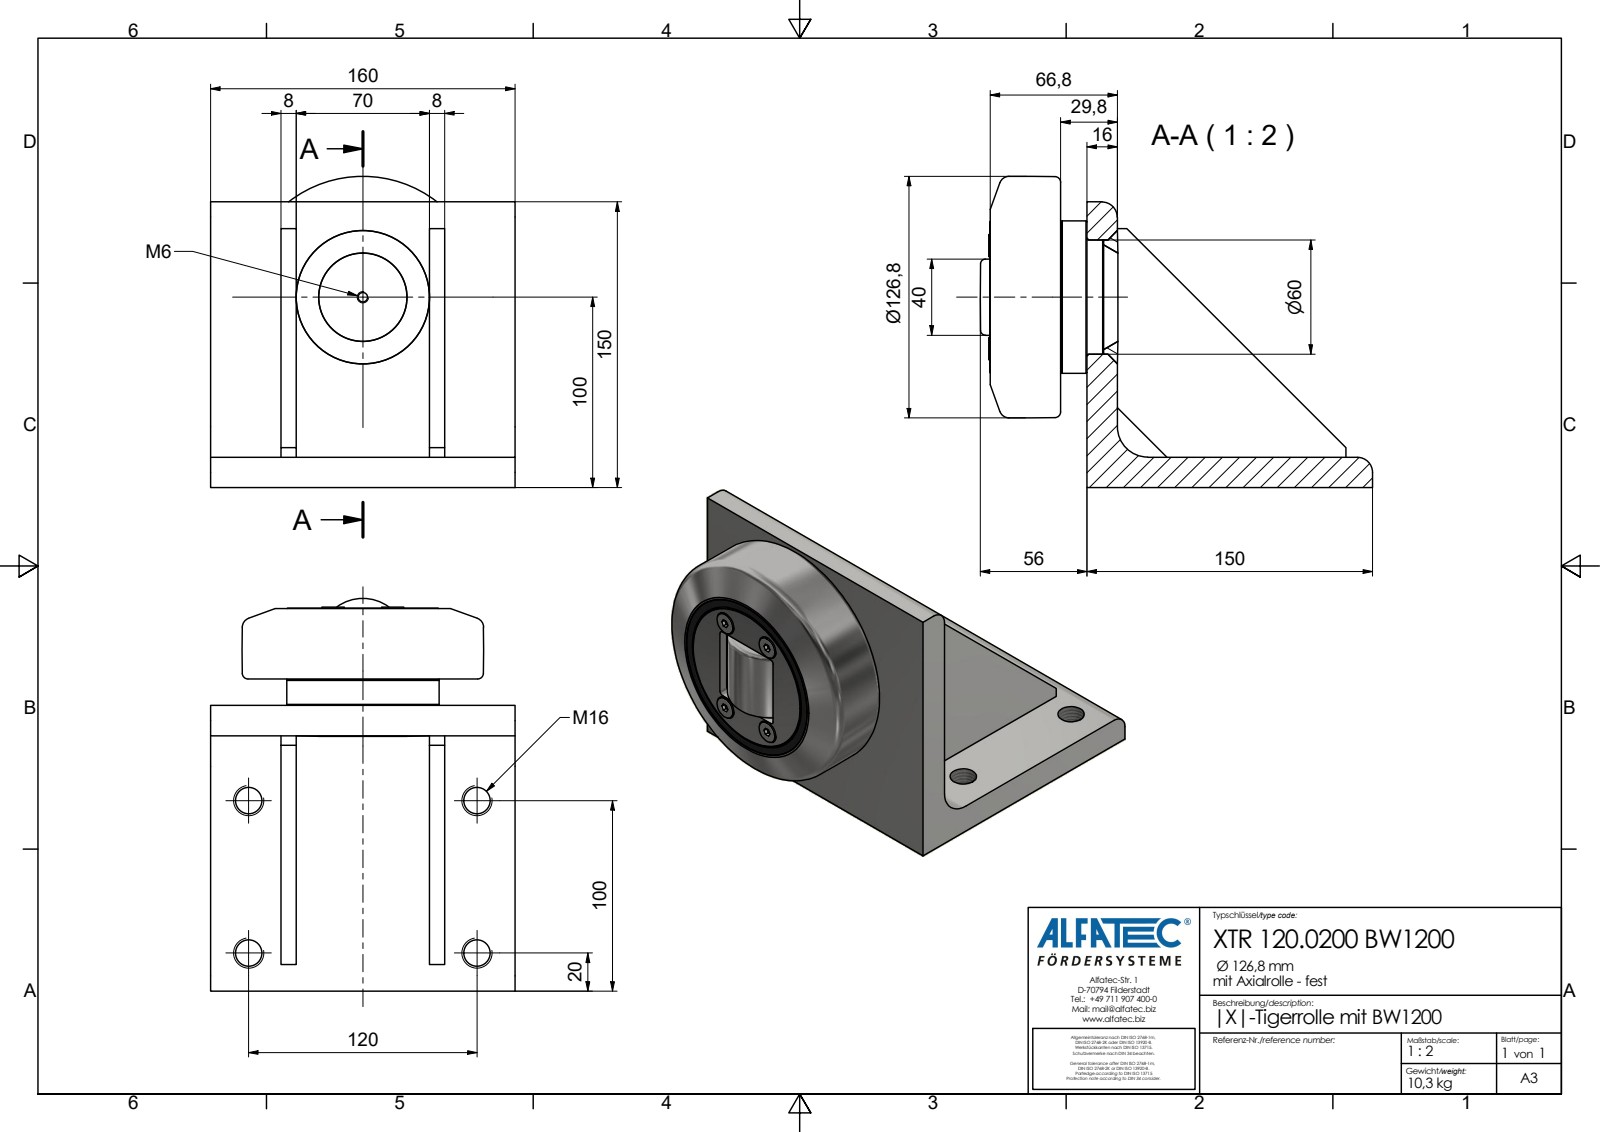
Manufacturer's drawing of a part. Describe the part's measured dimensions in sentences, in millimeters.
The part is named "XTR 120.0200 BW1200_Kontur". Its 3-D file was written by "Autodesk Inventor 2020 (AP242_MANAGED_MODEL_BASED_3D_ENGINEERING_MIM_LF)". It is 1 solid with 93 faces: 64 planar, 14 cylindrical and 15 other. Overall it measures 206 by 163.4 by 160 millimeters. Its volume is 1 361 000 cubic millimeters and its surface area 165 743 square millimeters. Round holes: 4 of diameter 13.84, 1 of diameter 4.92. Round bosses or shafts: 4 of diameter 11.7, 1 of diameter 80. Partial cylindrical surfaces (rounded edges, fillets, slot ends): 2 of radius 8, 1 of radius 16. The main face-to-face distances are 16, 8, 78, 37, 45, 115, 123, 70, 86, 29.8. The hole center spacings are 80, 120, 144.22.
